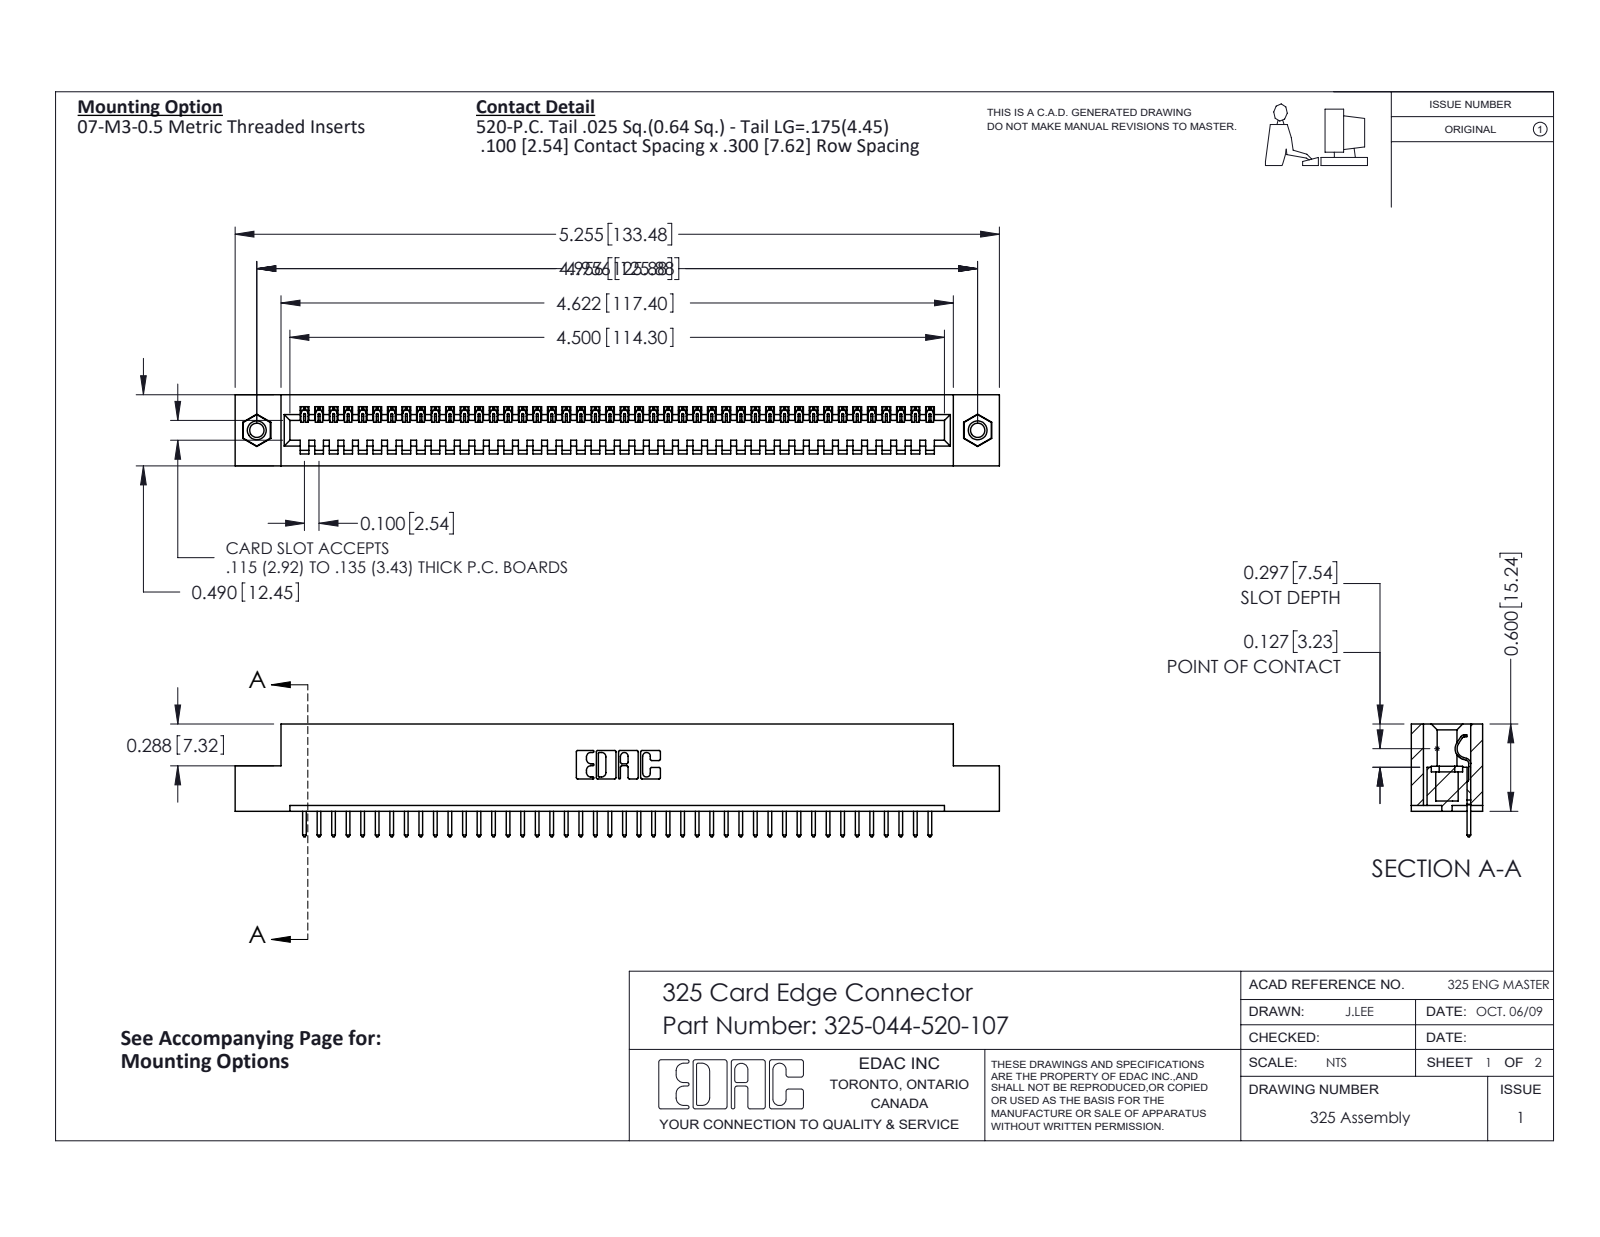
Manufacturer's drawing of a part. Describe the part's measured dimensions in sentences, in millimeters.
The part is named "325-044-520-107; 325-292-001_325-293-120; 345-250-001_345-250-005-103; 325 Part_TI". Its 3-D file was written by "SolidWorks 2016 (CONFIG_CONTROL_DESIGN)". It is 47 solids with 2726 faces: 1950 planar, 760 cylindrical and 16 other. Overall it measures 133.5 by 19.7 by 12.4 millimeters. Its volume is 16 830 cubic millimeters and its surface area 17 990 square millimeters. Round holes: 2 of diameter 2.5, 2 of diameter 3.2, 2 of diameter 4.1. Round bosses or shafts: 2 of diameter 3.9. Partial cylindrical surfaces (rounded edges, fillets, slot ends): 88 of radius 0.2, 88 of radius 0.3, 22 of radius 0.3, 6 of radius 0.2, 6 of radius 0.8, 3 of radius 0.7, 1 of radius 0.4, 1 of radius 0.6. The main face-to-face distances are 2.1, 10.3, 12.4, 7.6, 2.7, 9.7, 0.6, 8.3, 14.2, 1. The hole center spacings are 125.9.
